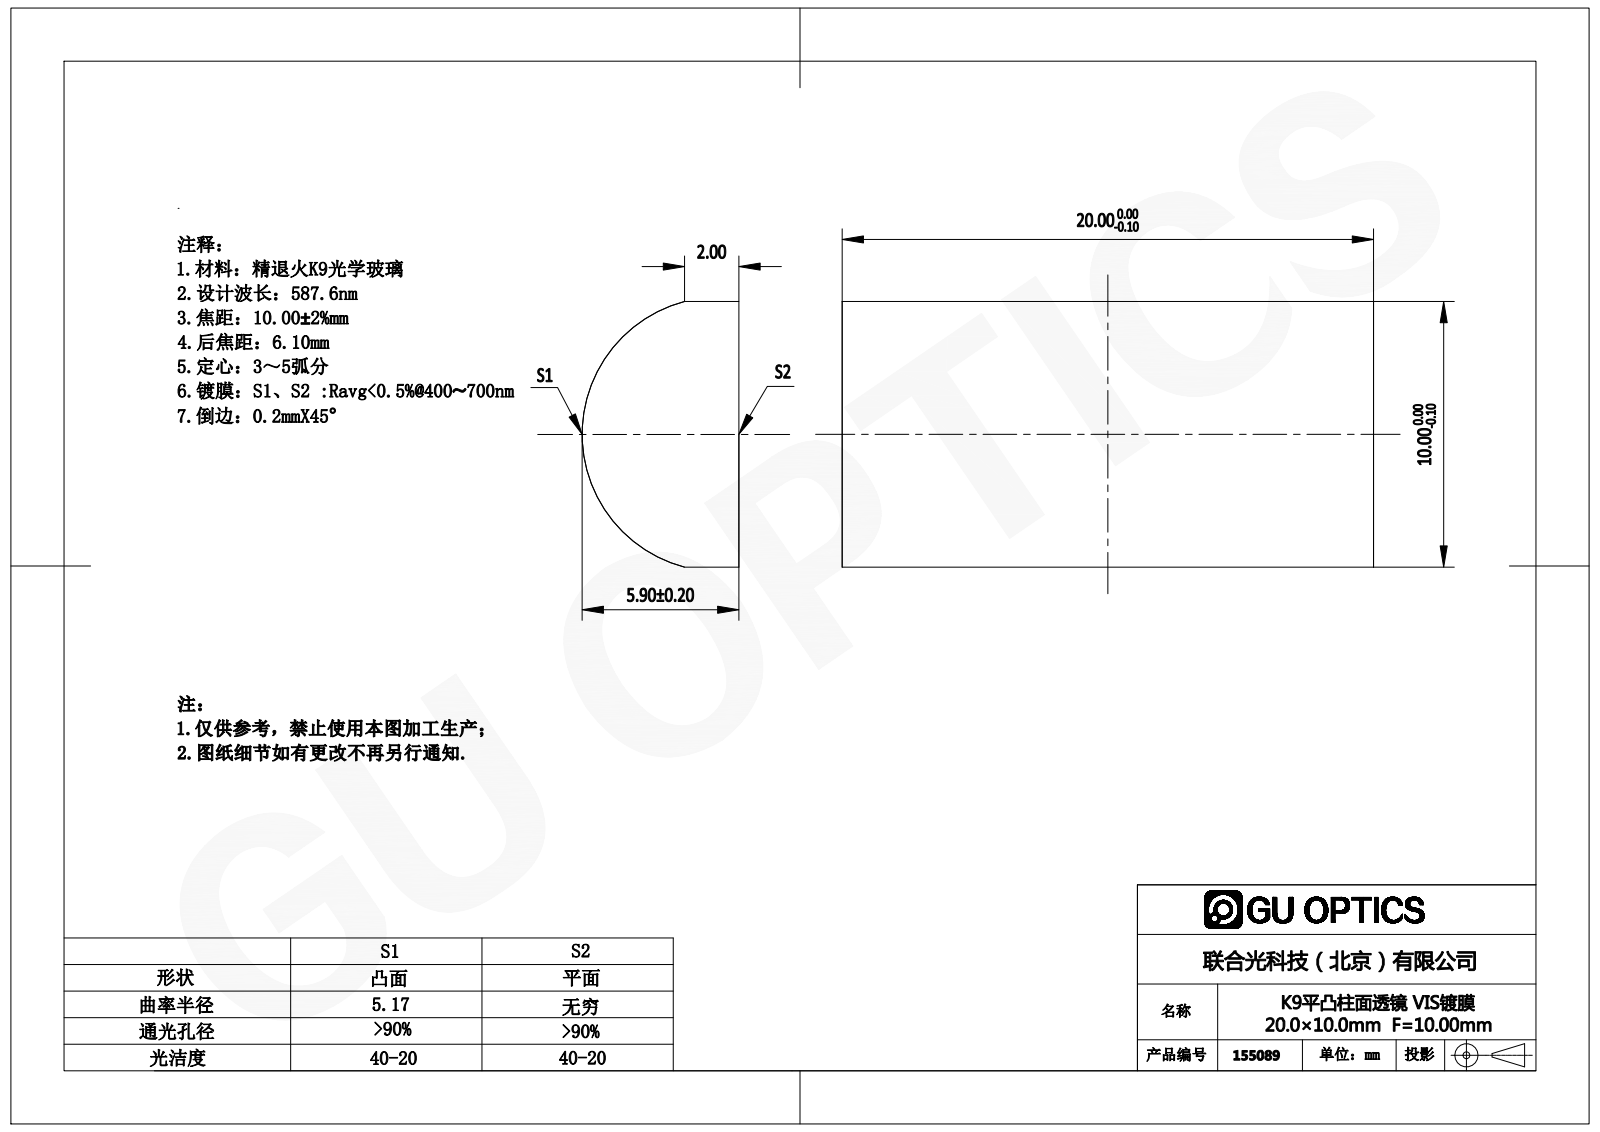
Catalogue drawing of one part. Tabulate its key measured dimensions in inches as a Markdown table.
| quantity | value |
| --- | --- |
| part name | 155023 |
| STEP written by | SolidWorks 2016 (AUTOMOTIVE_DESIGN) |
| units | inches |
| bodies | 1 solid, 6 faces (5 planar, 1 cylindrical, 0 other) |
| overall size | 0.787 × 0.394 × 0.232 |
| volume | 0.06 in³ |
| surface area | 1.01 in² |
| partial cylindrical surfaces (radius × count) | 0.204 × 1 |
| main face-to-face distances | 0.787, 0.394 |
